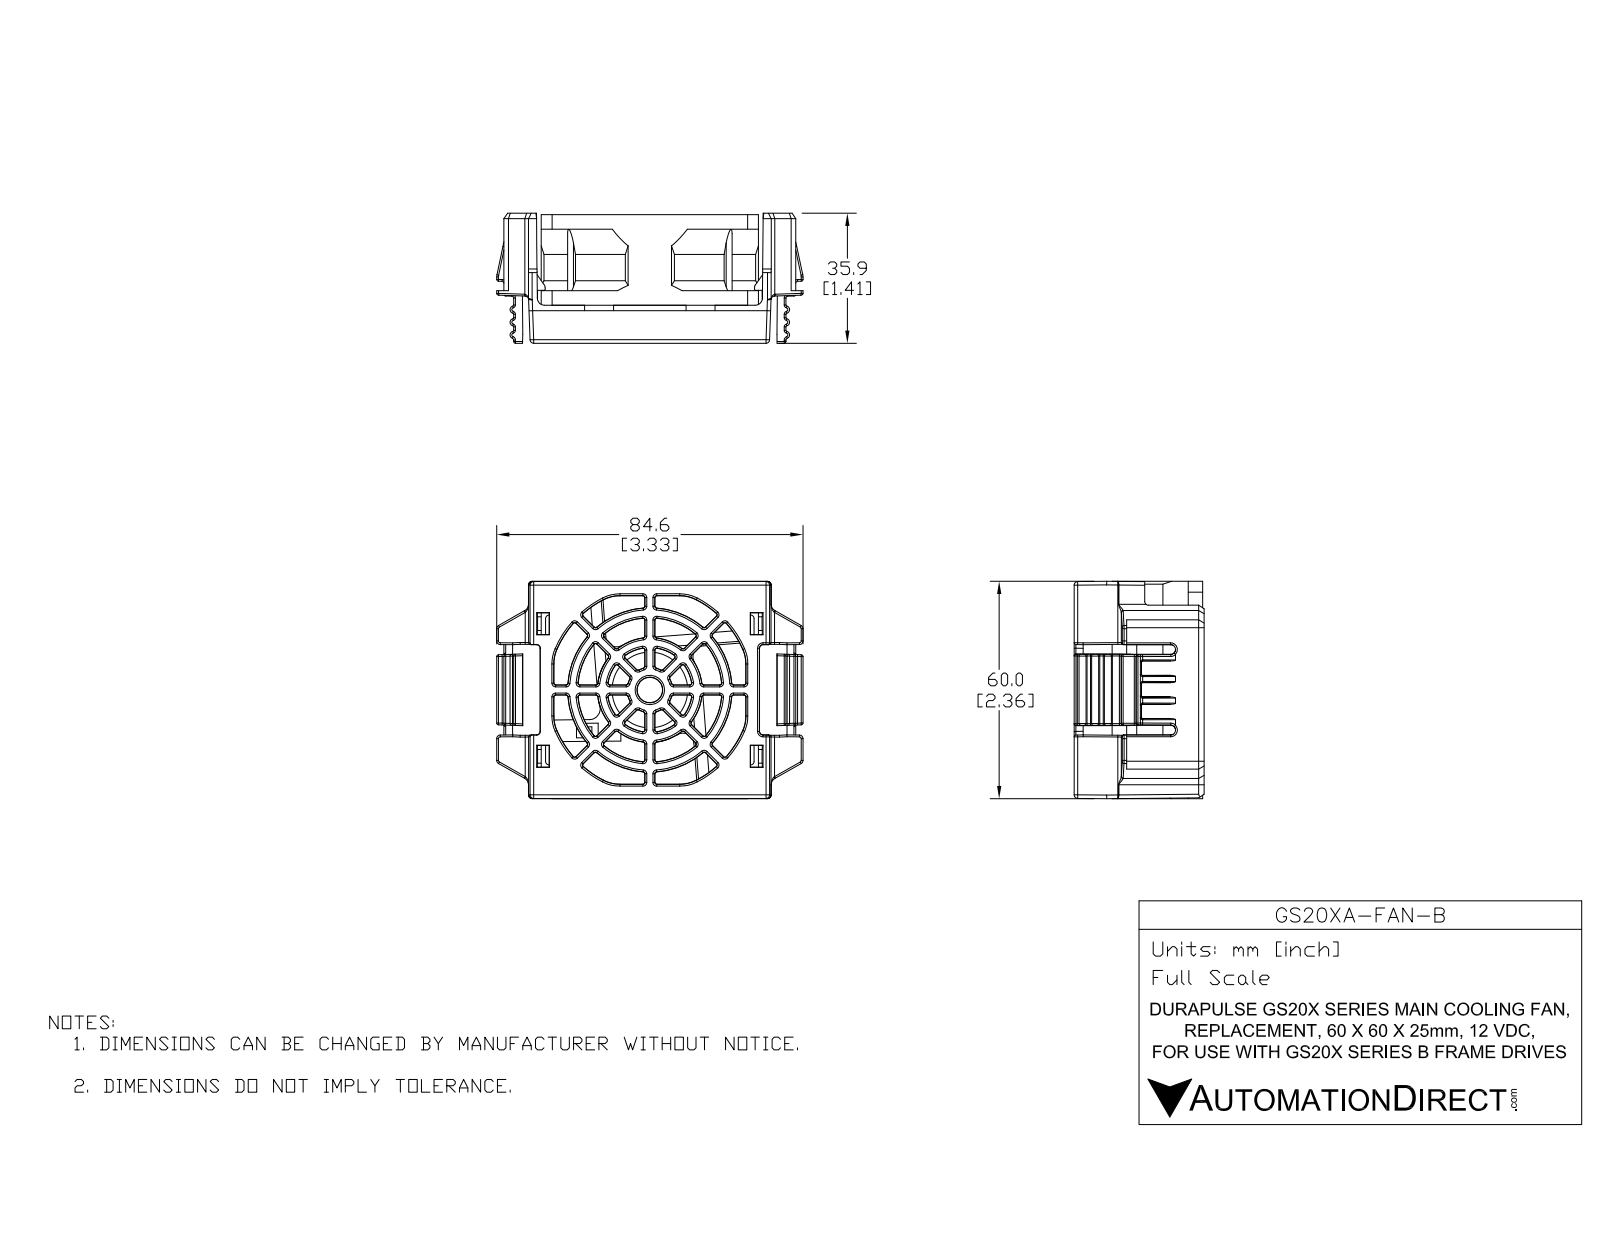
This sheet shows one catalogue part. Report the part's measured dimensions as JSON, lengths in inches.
{"part_name": "GS20XA-FAN-B", "step_written_by": "SolidWorks 2017 (AUTOMOTIVE_DESIGN)", "units": "inches", "bodies": {"solids": 2, "faces": 1667, "planar": 509, "cylindrical": 397, "other": 761}, "overall_size": [3.331, 2.362, 1.413], "volume_in3": 2.172, "surface_area_in2": 57.34, "round_holes": [[0.169, 4], [1.063, 1], [2.268, 1]], "round_bosses_or_shafts": [[0.823, 1]], "partial_cylinders_radius": [[0.02, 110], [0.039, 51], [0.012, 38], [0.016, 10], [0.118, 10], [0.079, 6], [0.197, 6], [0.037, 4]], "face_to_face_distances": [0.098, 2.362, 0.047, 2.315, 1.299, 1.398, 0.827, 0.157, 0.406, 2.768], "hole_center_spacings": [1.392, 1.392, 1.968, 1.969, 2.783]}
